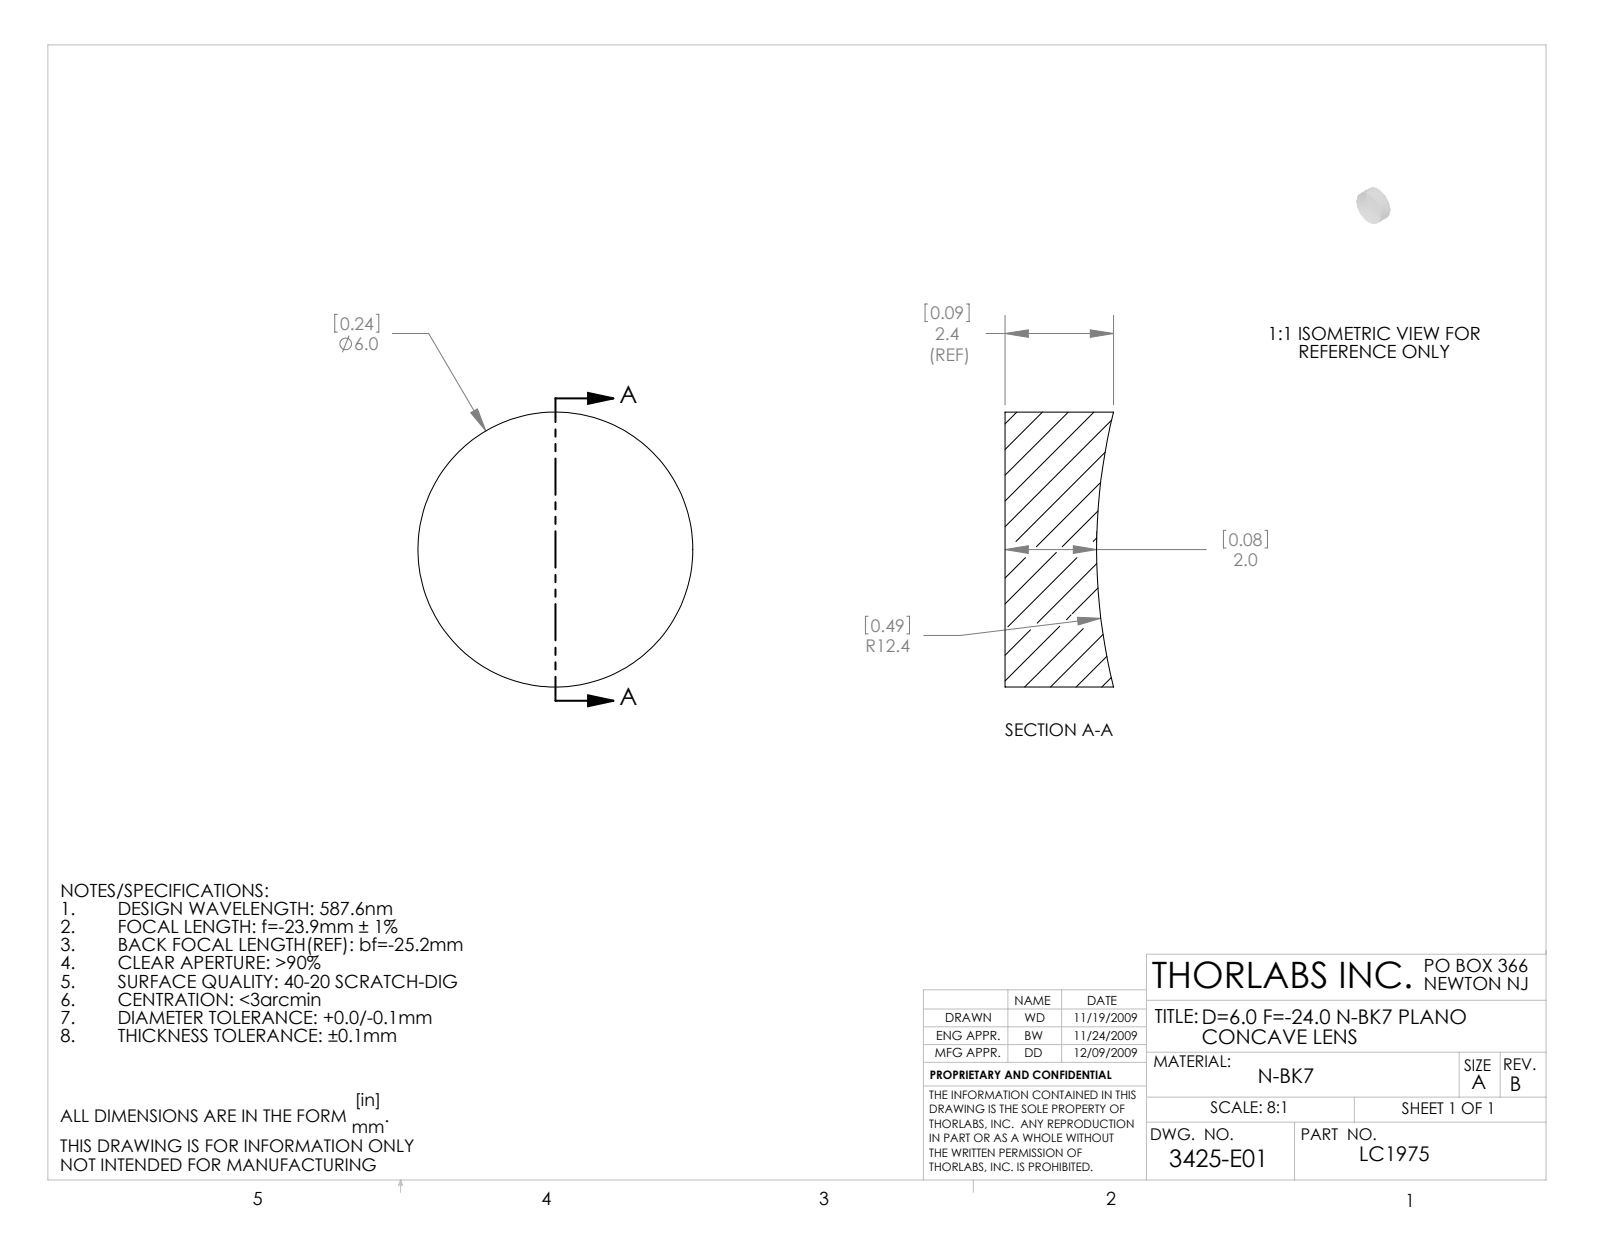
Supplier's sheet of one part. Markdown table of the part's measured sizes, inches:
| quantity | value |
| --- | --- |
| part name | 3425-E0W |
| STEP written by | SolidWorks 2009 (AUTOMOTIVE_DESIGN) |
| units | inches |
| bodies | 1 solid, 5 faces (1 planar, 2 cylindrical, 2 other) |
| overall size | 0.236 × 0.236 × 0.093 |
| volume | 0.004 in³ |
| surface area | 0.158 in² |
| round bosses / shafts (diameter × count) | 0.236 × 1 |
